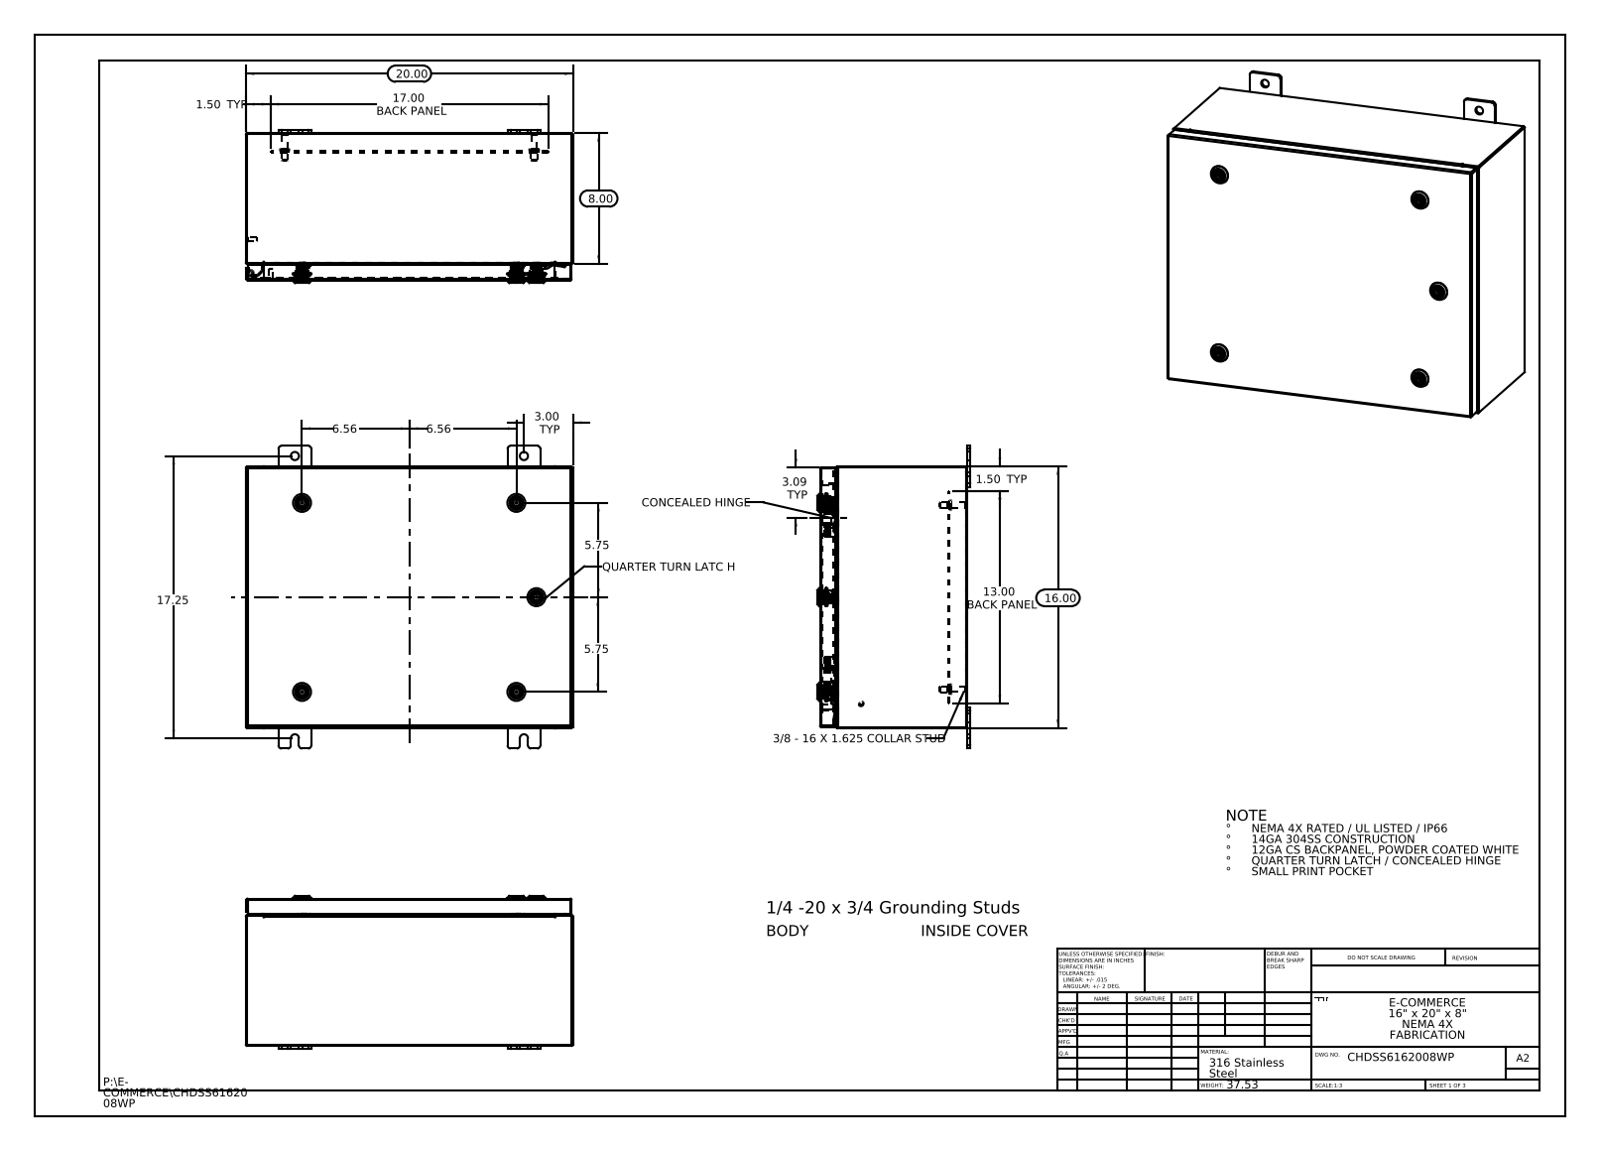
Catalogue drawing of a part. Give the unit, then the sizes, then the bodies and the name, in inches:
Units: inches
Overall size (bounding box): 20 × 18.5 × 9.356
Round holes (diameter × count): ⌀0.5 ×8, ⌀0.197 ×5, ⌀0.394 ×5, ⌀0.4 ×5, ⌀0.63 ×5, ⌀0.787 ×5, ⌀0.136 ×4, ⌀0.211 ×1
Round bosses / shafts (diameter × count): ⌀0.236 ×7, ⌀1.102 ×5, ⌀0.78 ×5, ⌀0.626 ×5, ⌀0.61 ×5, ⌀0.531 ×5, ⌀0.392 ×5, ⌀0.114 ×5
Partial cylindrical surfaces — rounded edges, fillets, slot ends (radius × count): R0.006 ×165, R0.118 ×165, R0.028 ×60, R0.19 ×24, R0.02 ×20, R0.197 ×20, R0.013 ×18, R0.088 ×18
Main face-to-face distances: 0.075, 0.074, 15.925, 9.01, 8.935, 8.936, 8.861, 19.925, 1, 1.075
Hole centre spacings: 0.688, 1.858, 3.065, 5.627, 9.687, 11.25, 11.55, 13.015
Volume: 134.9 in³ · Surface area: 3 401 in²
Bodies: 49 solids, 4592 faces (1366 planar, 1436 cylindrical, 1790 other)
Part name (STEP PRODUCT): CHDSS6162008WP Bottom; HW-CLH-R001-0500_2412-026240-2445-Industrilas; CHDSS6162008WP Body; HW-CLH-E5-8004_Cam-232112-U-Industrilas (+8 more)
STEP written by: SolidWorks 2013 (CONFIG_CONTROL_DESIGN)
